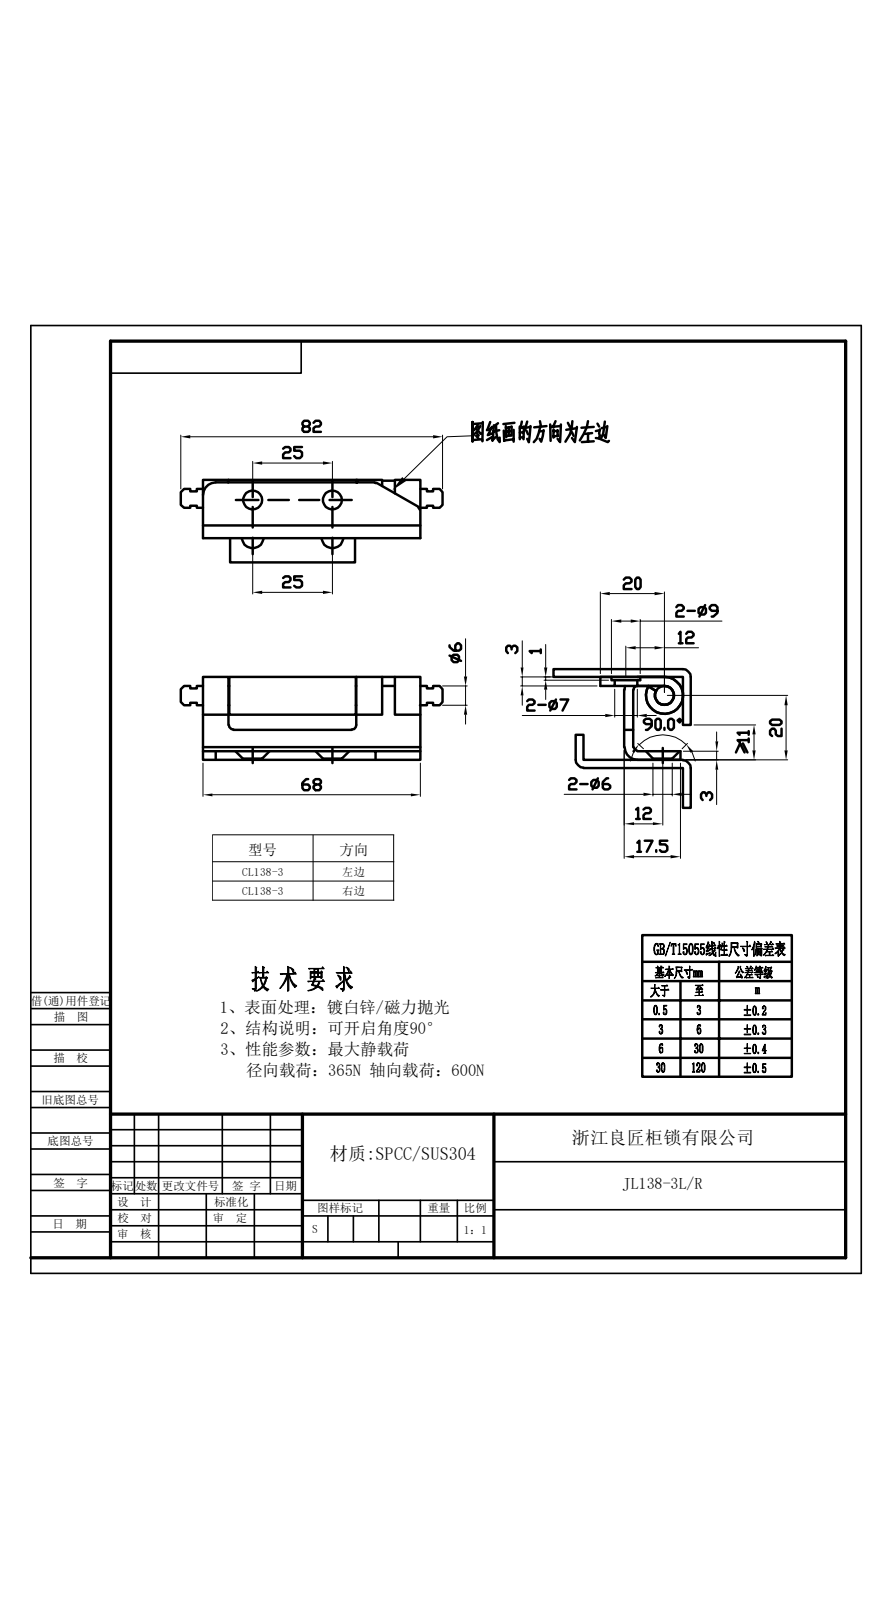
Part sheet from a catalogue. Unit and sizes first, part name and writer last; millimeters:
Units: millimetres
Overall size (bounding box): 87.12 × 82 × 26.6
Round holes (diameter × count): ⌀6 ×4, ⌀7 ×4, ⌀6.8 ×2
Round bosses / shafts (diameter × count): ⌀12.8 ×2, ⌀6 ×2, ⌀4.5 ×2
Partial cylindrical surfaces — rounded edges, fillets, slot ends (radius × count): R4 ×10, R1 ×8, R1.2 ×4
Main face-to-face distances: 3, 23.6, 26.6, 2.8, 69.32, 20.6, 72.12, 66.52, 8, 60
Hole centre spacings: 11.5, 25, 27.52, 59.62, 64.65, 48.12, 54.23, 71.12
Volume: 30 633 mm³ · Surface area: 25 060 mm²
Bodies: 6 solids, 172 faces (66 planar, 82 cylindrical, 24 other)
STEP written by: Rhino 8.5 (CONFIG_CONTROL_DESIGN)
